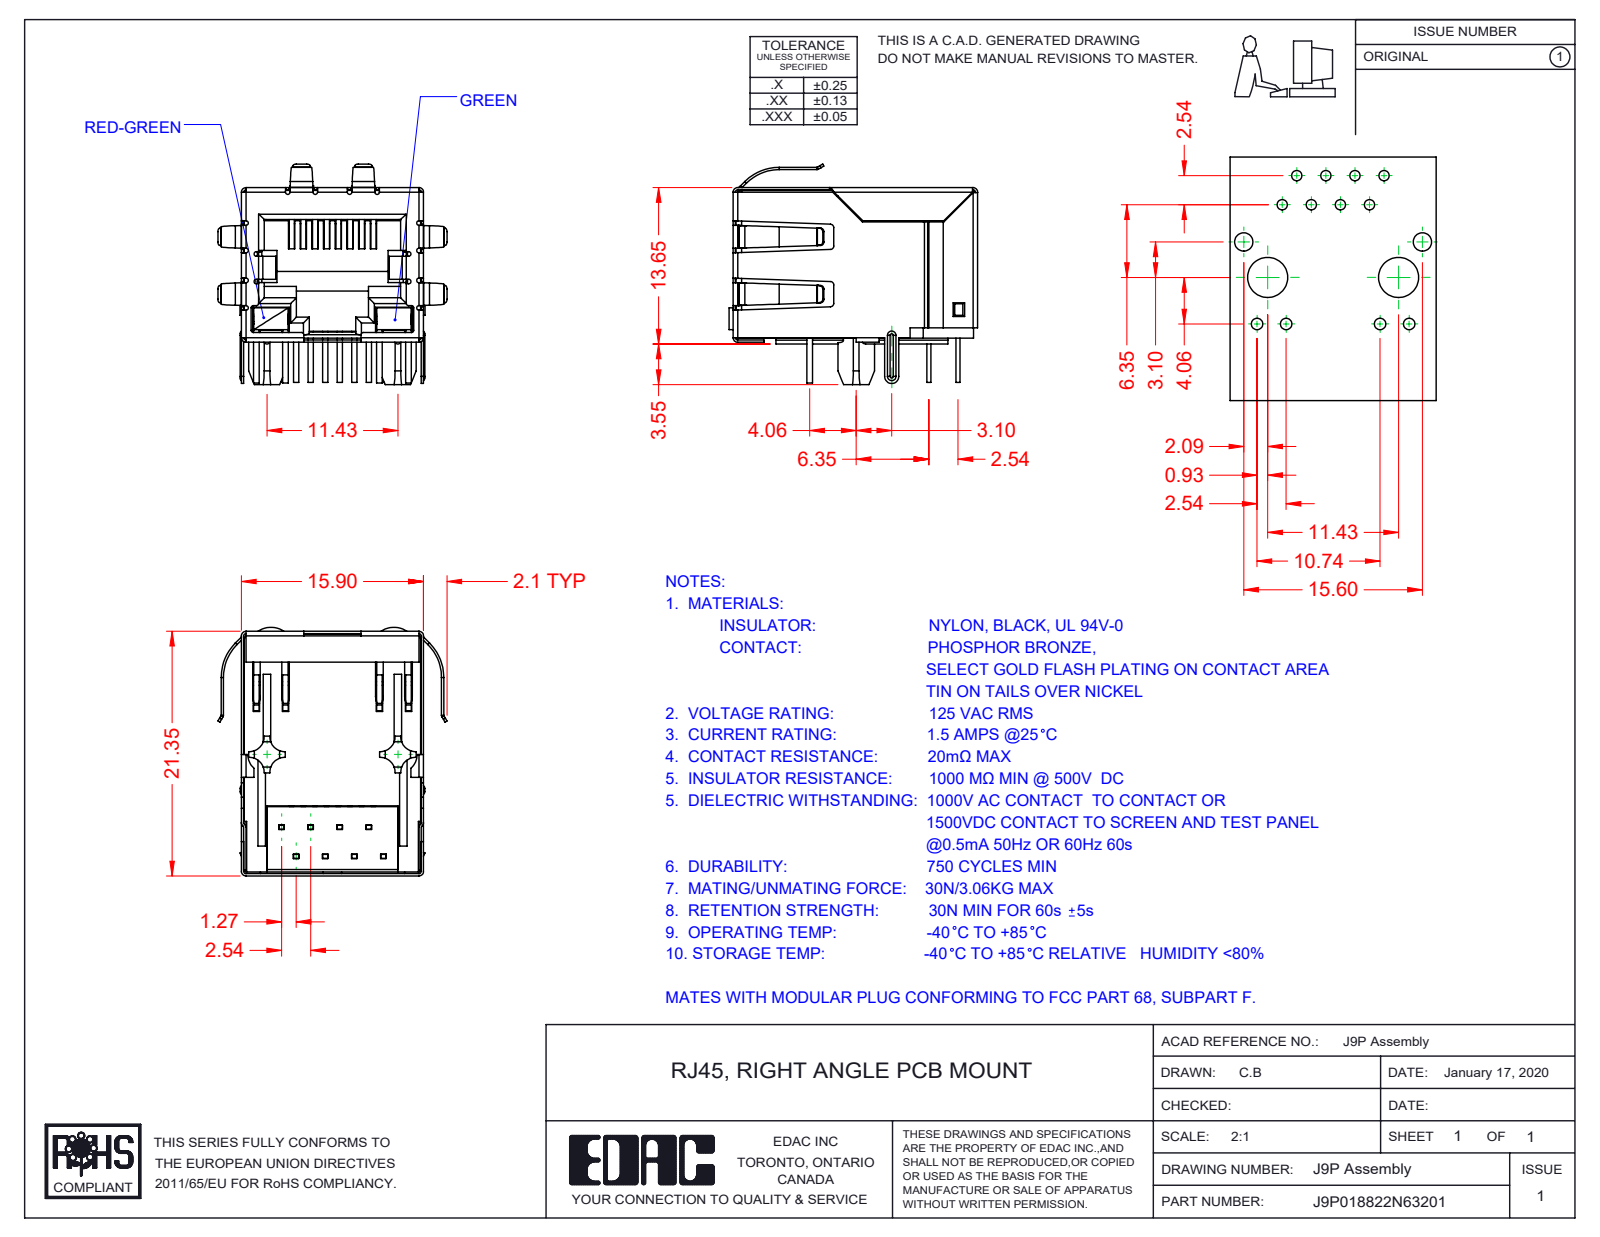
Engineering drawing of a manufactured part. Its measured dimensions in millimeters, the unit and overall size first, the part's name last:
Units: millimetres
Overall size (bounding box): 21.7 × 20 × 19.25
Partial cylindrical surfaces — rounded edges, fillets, slot ends (radius × count): R0.2 ×39, R0.5 ×22, R0.3 ×20, R0.4 ×16, R1.3 ×8, R0.23 ×5, R0.11 ×4, R0.31 ×4
Main face-to-face distances: 15.45, 15.7, 15.65, 0.35, 0.54, 15.5, 12.36, 0.6, 1.4, 0.59
Volume: 2 687 mm³ · Surface area: 7 515 mm²
Bodies: 13 solids, 1474 faces (1042 planar, 338 cylindrical, 94 other)
Part name (STEP PRODUCT): 9P-LED Insulator; 9P-LED LED RH_3-Green; 9P-LED Shield; 9P-LED LED LH_6-Red-Green (+4 more)
STEP written by: SolidWorks 2016 (CONFIG_CONTROL_DESIGN)
